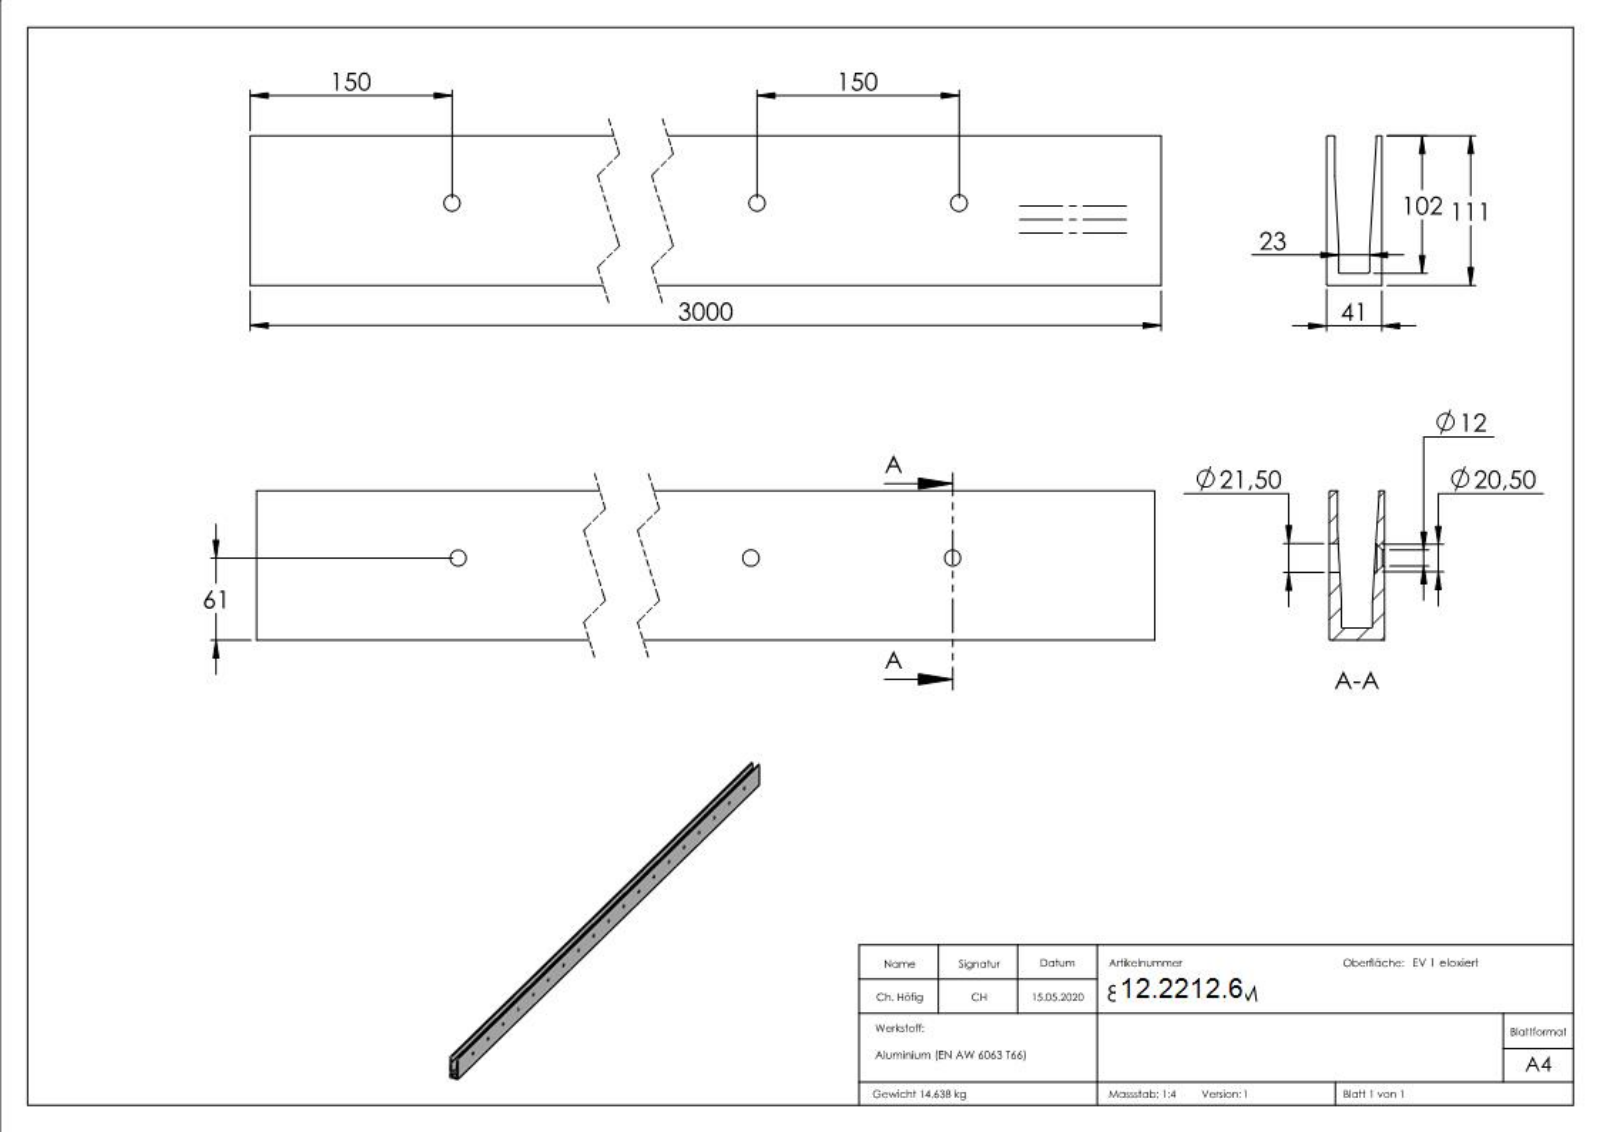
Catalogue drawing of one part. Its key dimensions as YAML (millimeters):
part_name: "80300-ALU-3M"
step_written_by: "SolidWorks 2015 (CONFIG_CONTROL_DESIGN)"
units: millimeters
bodies: {solids: 1, faces: 432, planar: 146, cylindrical: 121, other: 165}
overall_size: [3000, 111, 41]
volume: 5422000
surface_area: 1495000
round_holes:
  - {diameter: 12, count: 19}
  - {diameter: 20.5, count: 19}
  - {diameter: 21.5, count: 19}
partial_cylinders:
  - {radius: 0.65, count: 2}
  - {radius: 1, count: 2}
  - {radius: 1.2, count: 2}
face_to_face_distances: [41, 9, 32, 6.2, 34.8, 2.8, 25.8, 23, 111, 102]
hole_center_spacings: [150, 300, 450, 600, 750, 900, 1050, 1200]
